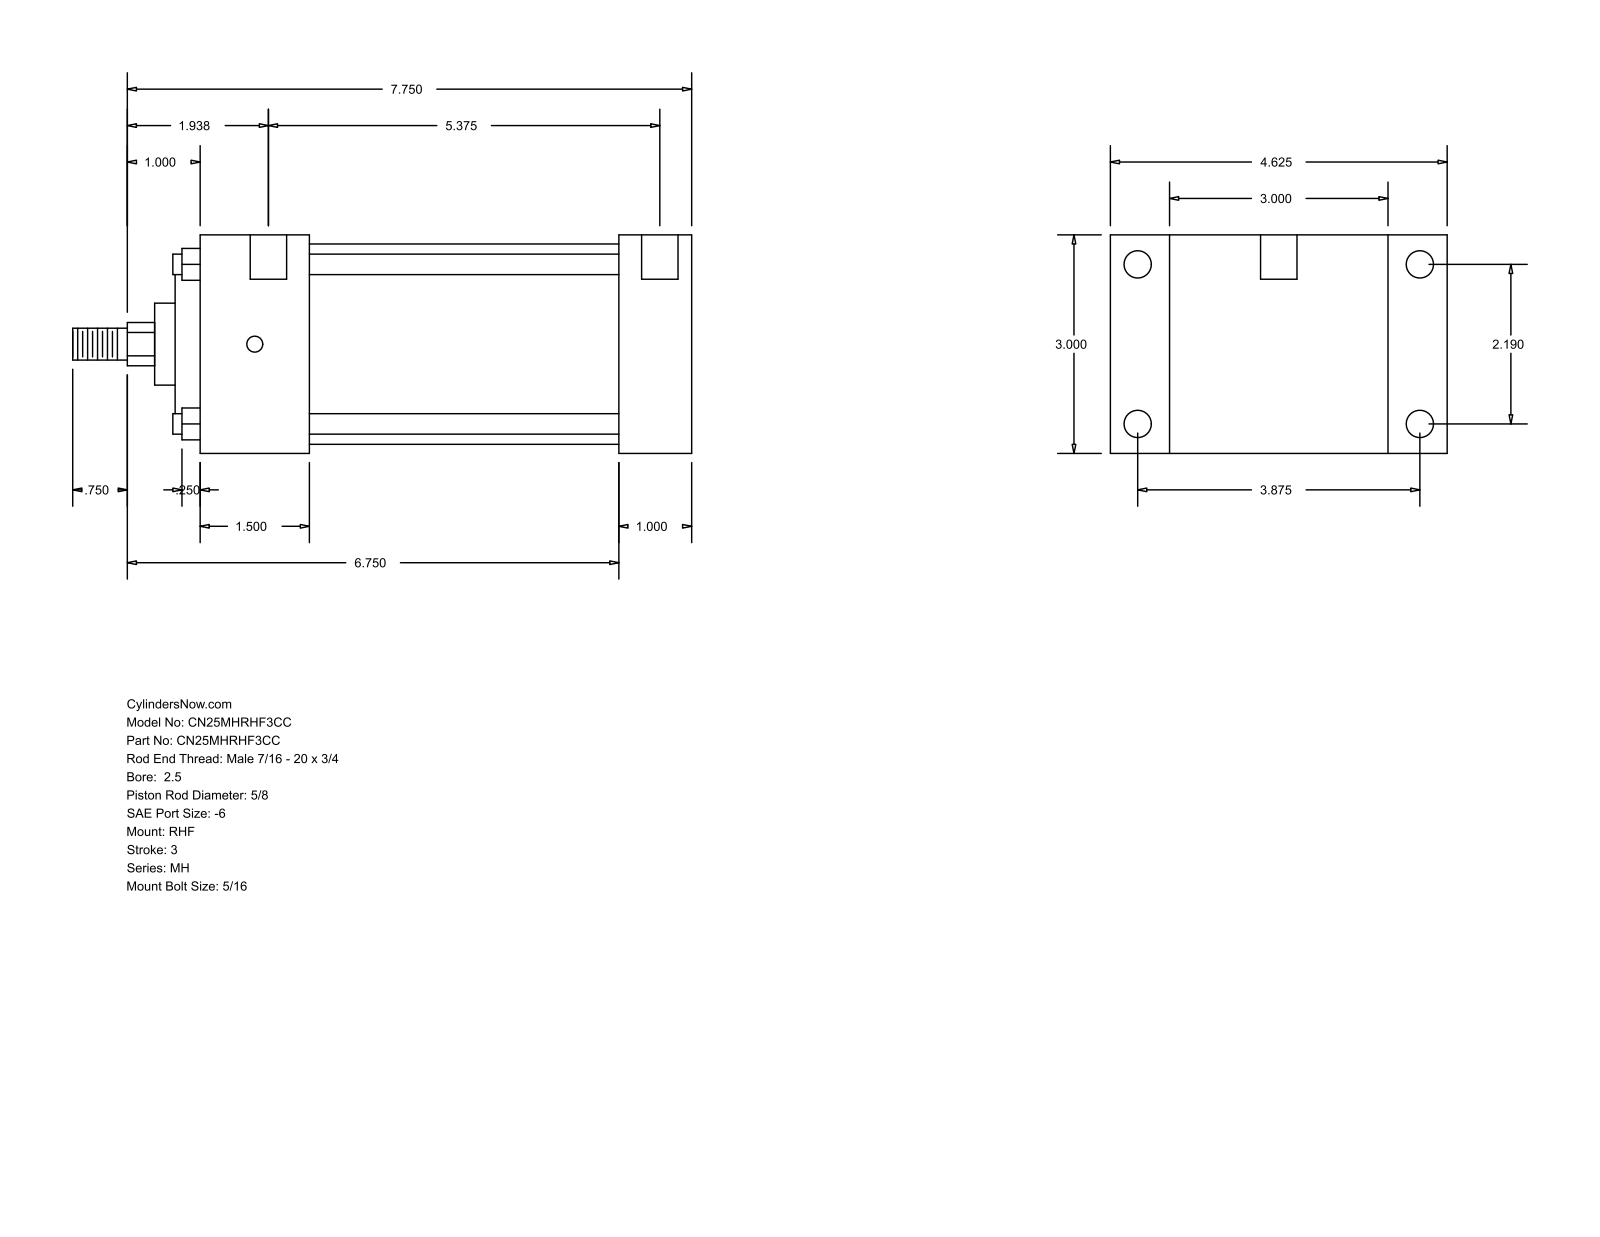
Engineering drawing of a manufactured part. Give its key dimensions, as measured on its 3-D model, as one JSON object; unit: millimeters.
{"part_name": "MH_RHF__0250_0.625", "step_written_by": "GSSL Pune (CONFIG_CONTROL_DESIGN)", "units": "millimeters", "bodies": {"solids": 0, "faces": 90, "planar": 61, "cylindrical": 29, "other": 0}, "overall_size": [215.9, 117.47, 76.2], "round_holes": [[5.56, 4], [9.53, 4], [12.7, 2]], "round_bosses_or_shafts": [[7.14, 4], [69.85, 1], [55.55, 1], [28.57, 1], [15.88, 1], [11.11, 1]], "partial_cylinders_radius": [[7.54, 1]], "face_to_face_distances": [76.2, 25.4, 20.64, 96.84, 171.45, 146.05, 38.1, 117.48, 107.95, 133.35], "hole_center_spacings": [55.62, 98.42, 113.05, 144.46, 3.17, 4.76, 136.53, 139.7]}
